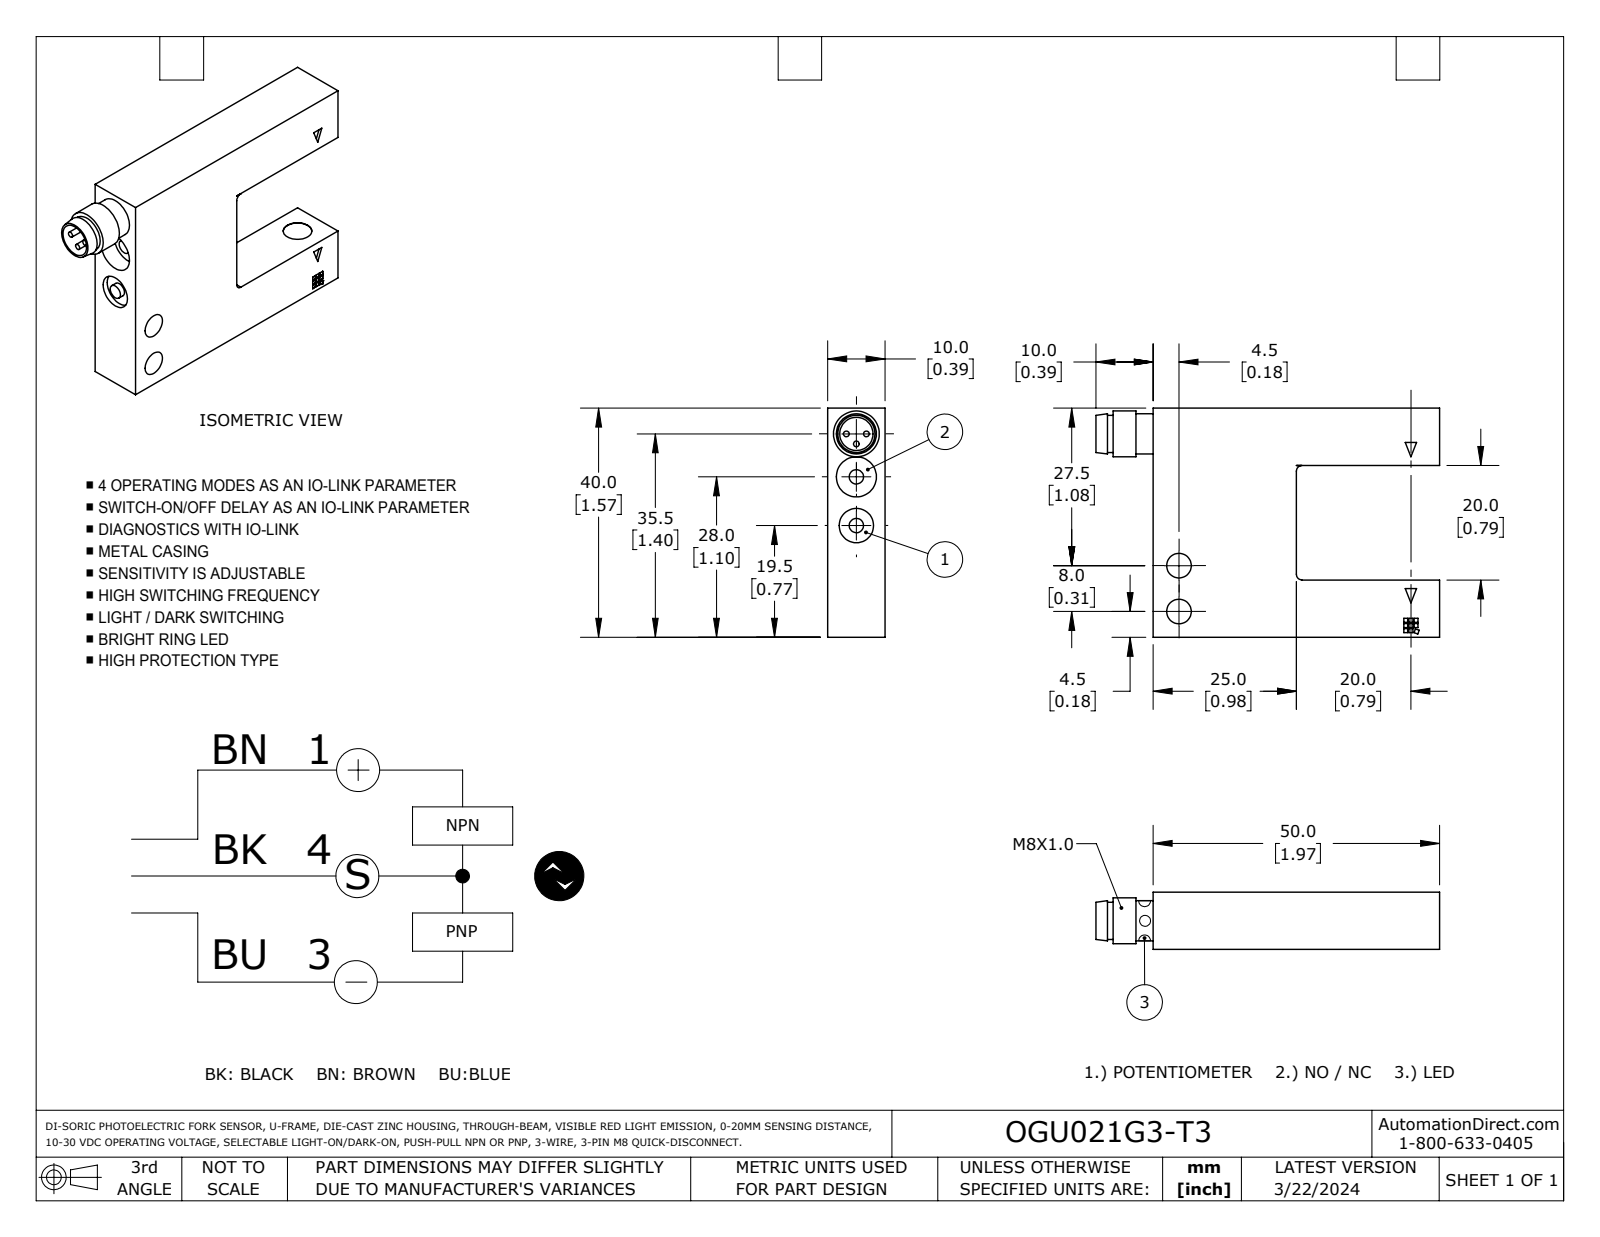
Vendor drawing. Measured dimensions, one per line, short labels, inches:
name: OGU021G3-T3
written by: SolidWorks 2023 (AUTOMOTIVE_DESIGN)
unit: in
bodies: 1 solid, 111 faces (91 planar, 19 cylindrical, 1 other)
size: 2.362 × 1.575 × 0.394
volume: 0.907 in³; area: 9.364 in²
holes: 2× ⌀0.169, 1× ⌀0.118, 1× ⌀0.197, 1× ⌀0.228, 1× ⌀0.236, 1× ⌀0.276
bosses: 3× ⌀0.039, 2× ⌀0.098, 1× ⌀0.315, 1× ⌀0.276, 1× ⌀0.256
rounds: 3× R0.039
face distances: 0.394, 1.575, 1.181, 0.984, 0.787, 1.969, 0.392, 0.039, 1.183, 0.789
hole spacings: 0.295, 0.315, 0.335, 0.63
